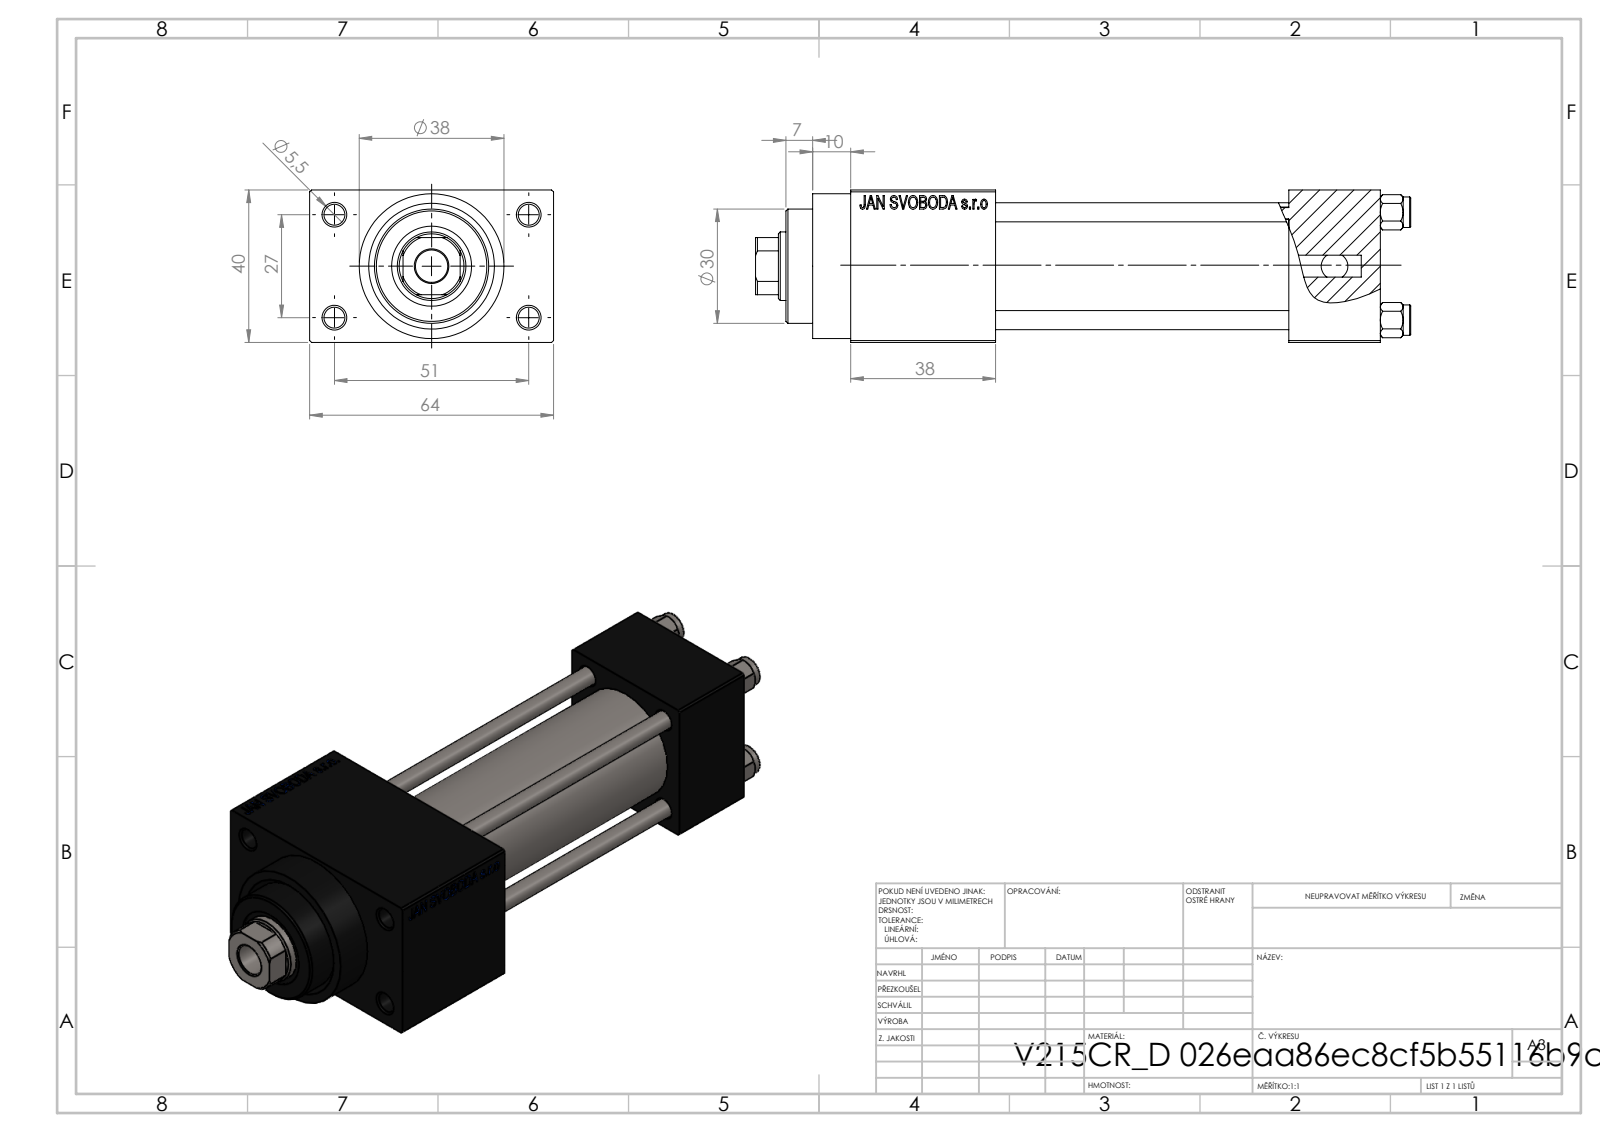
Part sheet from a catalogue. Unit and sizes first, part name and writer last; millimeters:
Units: millimetres
Overall size (bounding box): 172 × 64 × 40
Round holes (diameter × count): ⌀5 ×4, ⌀5.5 ×4, ⌀20 ×3, ⌀7 ×2, ⌀13.16 ×2, ⌀8.5 ×1, ⌀18 ×1, ⌀21 ×1, ⌀25 ×1, ⌀30 ×1
Round bosses / shafts (diameter × count): ⌀8 ×4, ⌀38 ×1, ⌀31 ×1
Partial cylindrical surfaces — rounded edges, fillets, slot ends (radius × count): R8.5 ×1
Main face-to-face distances: 40, 12, 77, 24, 101, 52, 38, 139, 115, 64
Hole centre spacings: 11.37, 20.01, 28.3, 28.85, 29.89, 39.66, 48.34, 27
Volume: 197 029 mm³ · Surface area: 73 489 mm²
Bodies: 11 solids, 1101 faces (495 planar, 86 cylindrical, 520 other)
Part name (STEP PRODUCT): V215CR_VCP_D; V215CR_D_Body; V215CR_D_TYCINKA; NUT_M5_D (+1 more)
STEP written by: SolidWorks 2019 (CONFIG_CONTROL_DESIGN)
